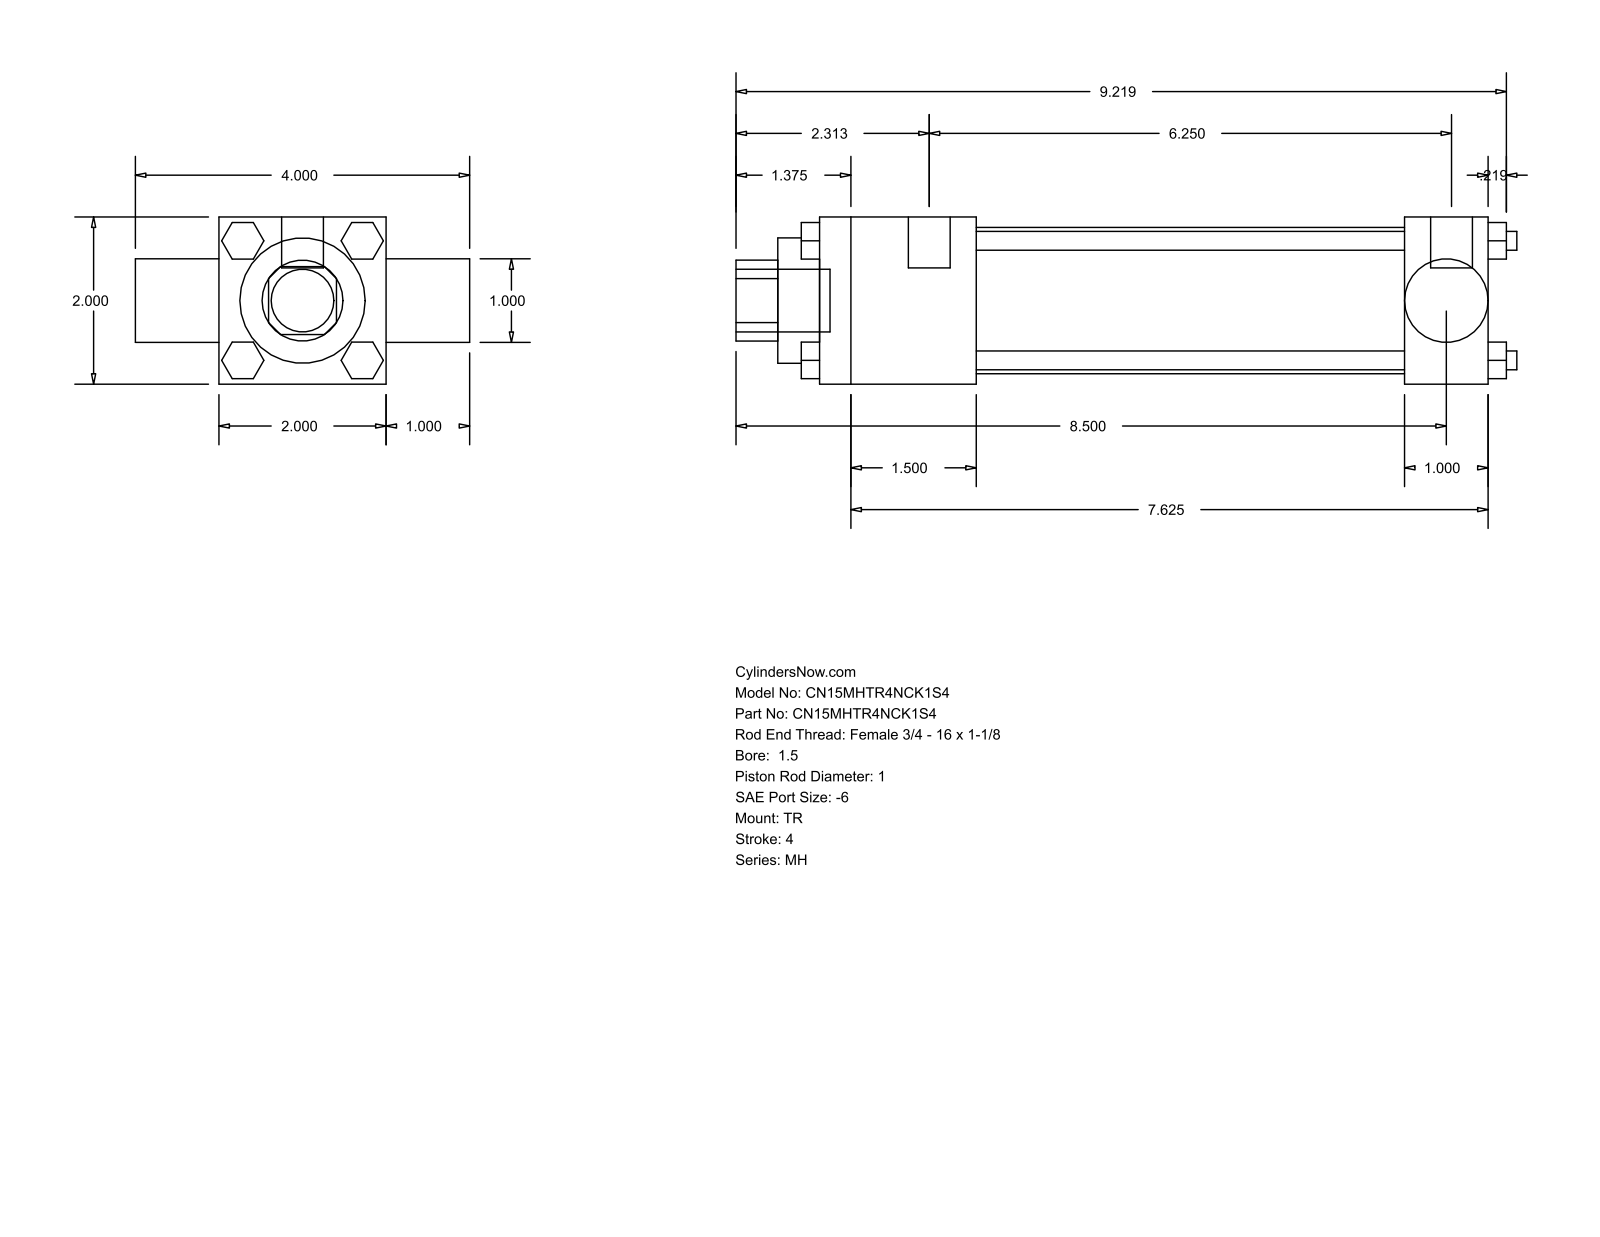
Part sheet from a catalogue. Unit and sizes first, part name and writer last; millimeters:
Units: millimetres
Overall size (bounding box): 237.33 × 101.6 × 50.8
Round holes (diameter × count): ⌀25.35 ×1, ⌀25.4 ×1, ⌀38.1 ×1, ⌀44.45 ×1
Round bosses / shafts (diameter × count): ⌀5.71 ×4, ⌀5.56 ×3, ⌀12.7 ×2, ⌀19.05 ×1
Partial cylindrical surfaces — rounded edges, fillets, slot ends (radius × count): R12.29 ×1
Main face-to-face distances: 50.8, 25.4, 203.2, 76.2, 47.63, 155.57, 177.8, 130.17, 208.76, 12.7
Bodies: 0 solids, 120 faces (92 planar, 28 cylindrical, 0 other)
Part name (STEP PRODUCT): MH_TR__0150_1
STEP written by: GSSL Pune (CONFIG_CONTROL_DESIGN)
